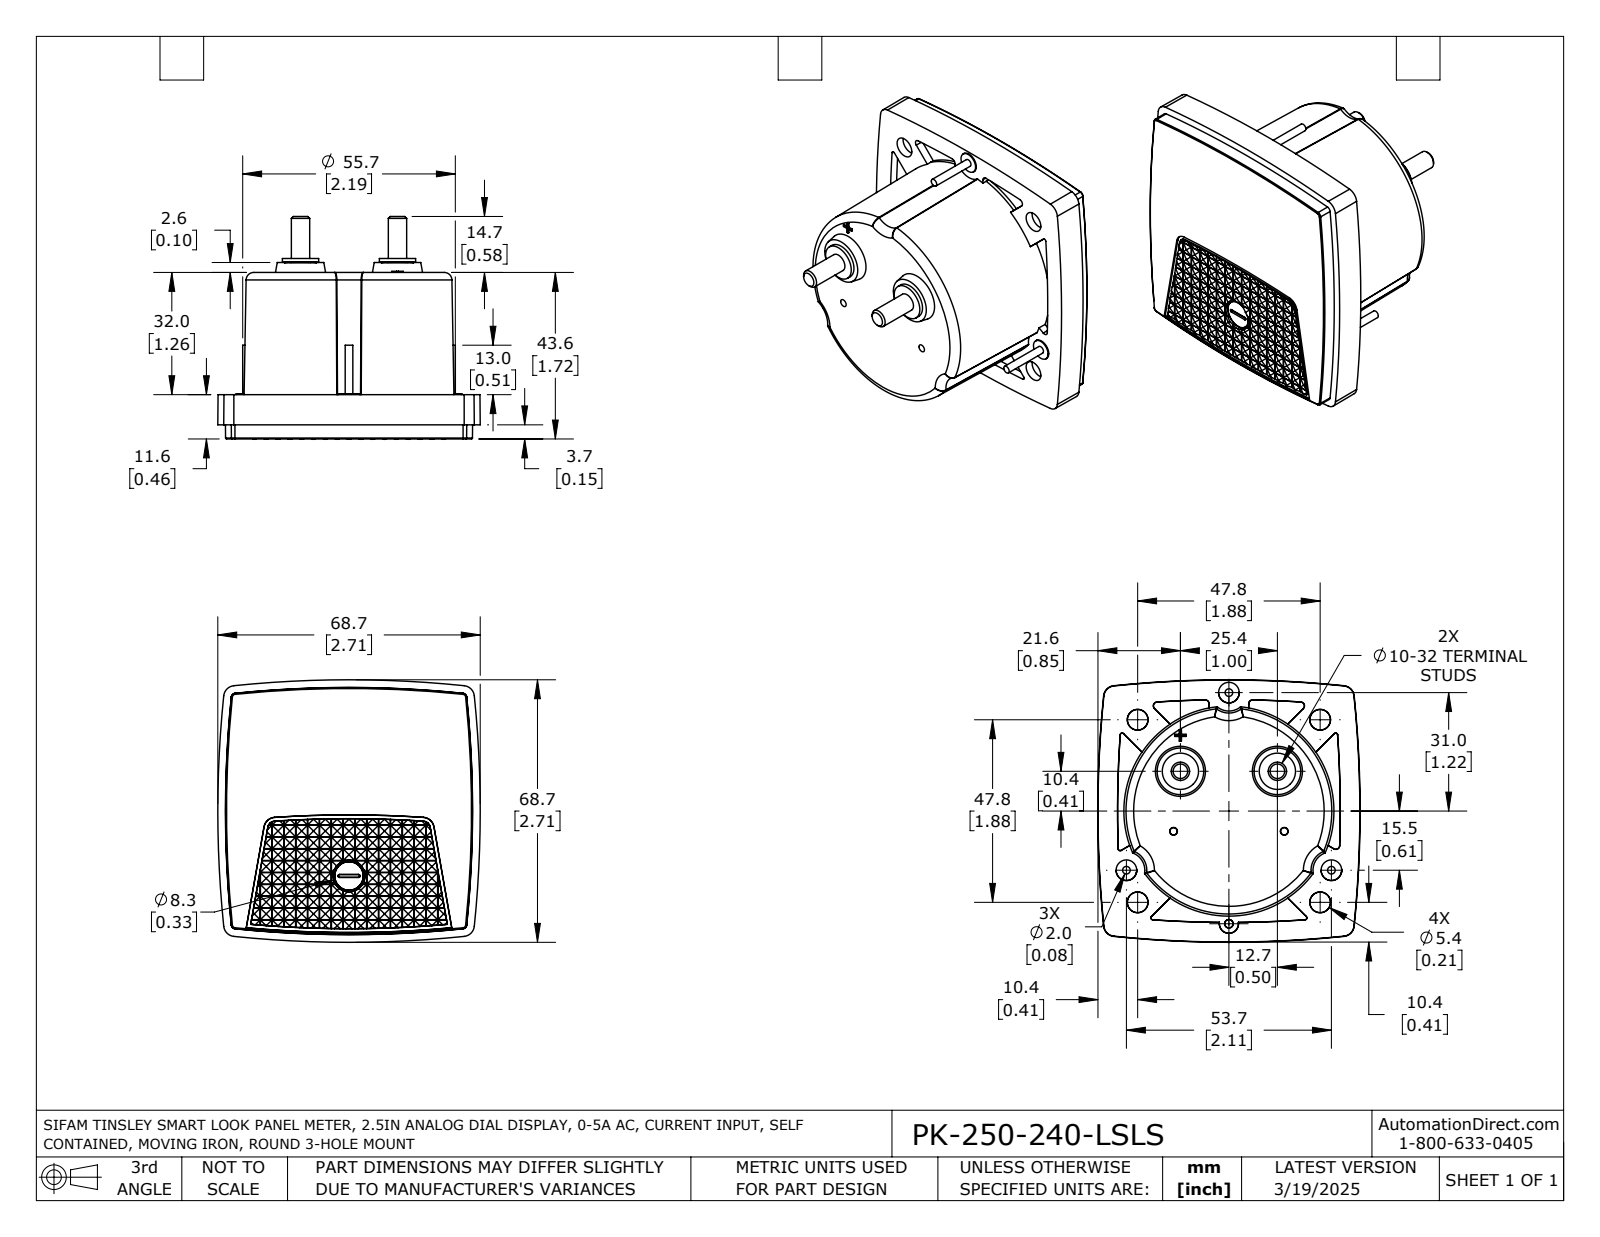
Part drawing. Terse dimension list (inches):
name: PK-250-240-LSLS
written by: SolidWorks 2021 (AUTOMOTIVE_DESIGN)
unit: in
bodies: 1 solid, 1550 faces (1165 planar, 265 cylindrical, 120 other)
size: 2.706 × 2.706 × 2.297
volume: 7.594 in³; area: 30.41 in²
bosses: 3× ⌀0.213, 3× ⌀0.079, 2× ⌀0.374, 2× ⌀0.189, 1× ⌀0.215
rounds: 2× R0.167, 1× R1.083
face distances: 1.717, 1.26, 0.457, 0.024, 0.087, 0.096, 0.311, 0.12, 0.072, 1.346
